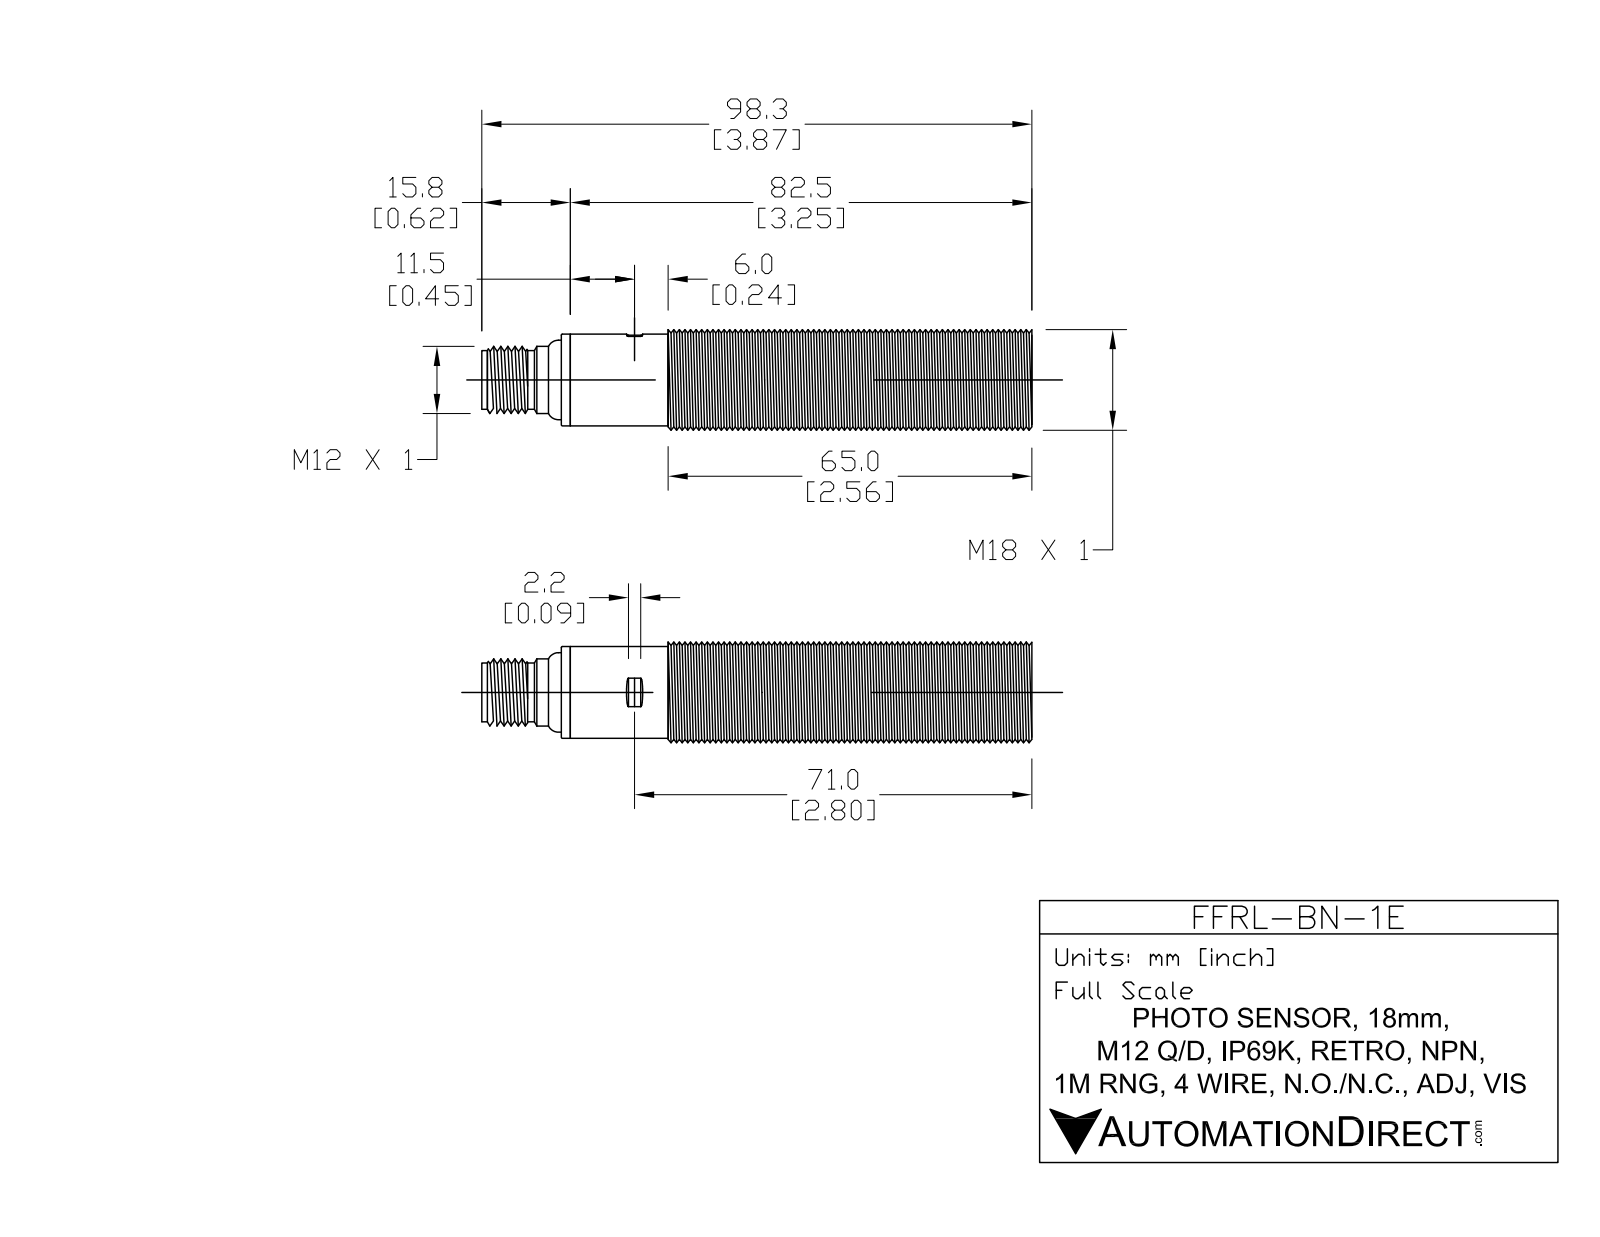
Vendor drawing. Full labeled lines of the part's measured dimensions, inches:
Part name (STEP PRODUCT): FFRL-BN-1E
STEP written by: SolidWorks 2017 (AUTOMOTIVE_DESIGN)
Units: inches
Bodies: 5 solids, 118 faces (21 planar, 48 cylindrical, 49 other)
Overall size (bounding box): 3.268 × 0.709 × 0.709
Volume: 1.081 in³ · Surface area: 10.47 in²
Round holes (diameter × count): ⌀0.278 ×1, ⌀0.327 ×1, ⌀0.5 ×1, ⌀0.583 ×1, ⌀0.61 ×1
Round bosses / shafts (diameter × count): ⌀0.039 ×4, ⌀0.709 ×1, ⌀0.646 ×1, ⌀0.612 ×1, ⌀0.604 ×1, ⌀0.559 ×1, ⌀0.492 ×1, ⌀0.472 ×1
Partial cylindrical surfaces — rounded edges, fillets, slot ends (radius × count): R0.024 ×1, R0.63 ×1
Main face-to-face distances: 2.539, 0.118, 2.657, 0.024, 0.094, 2.634, 2.717, 2.693, 2.598, 0.059
